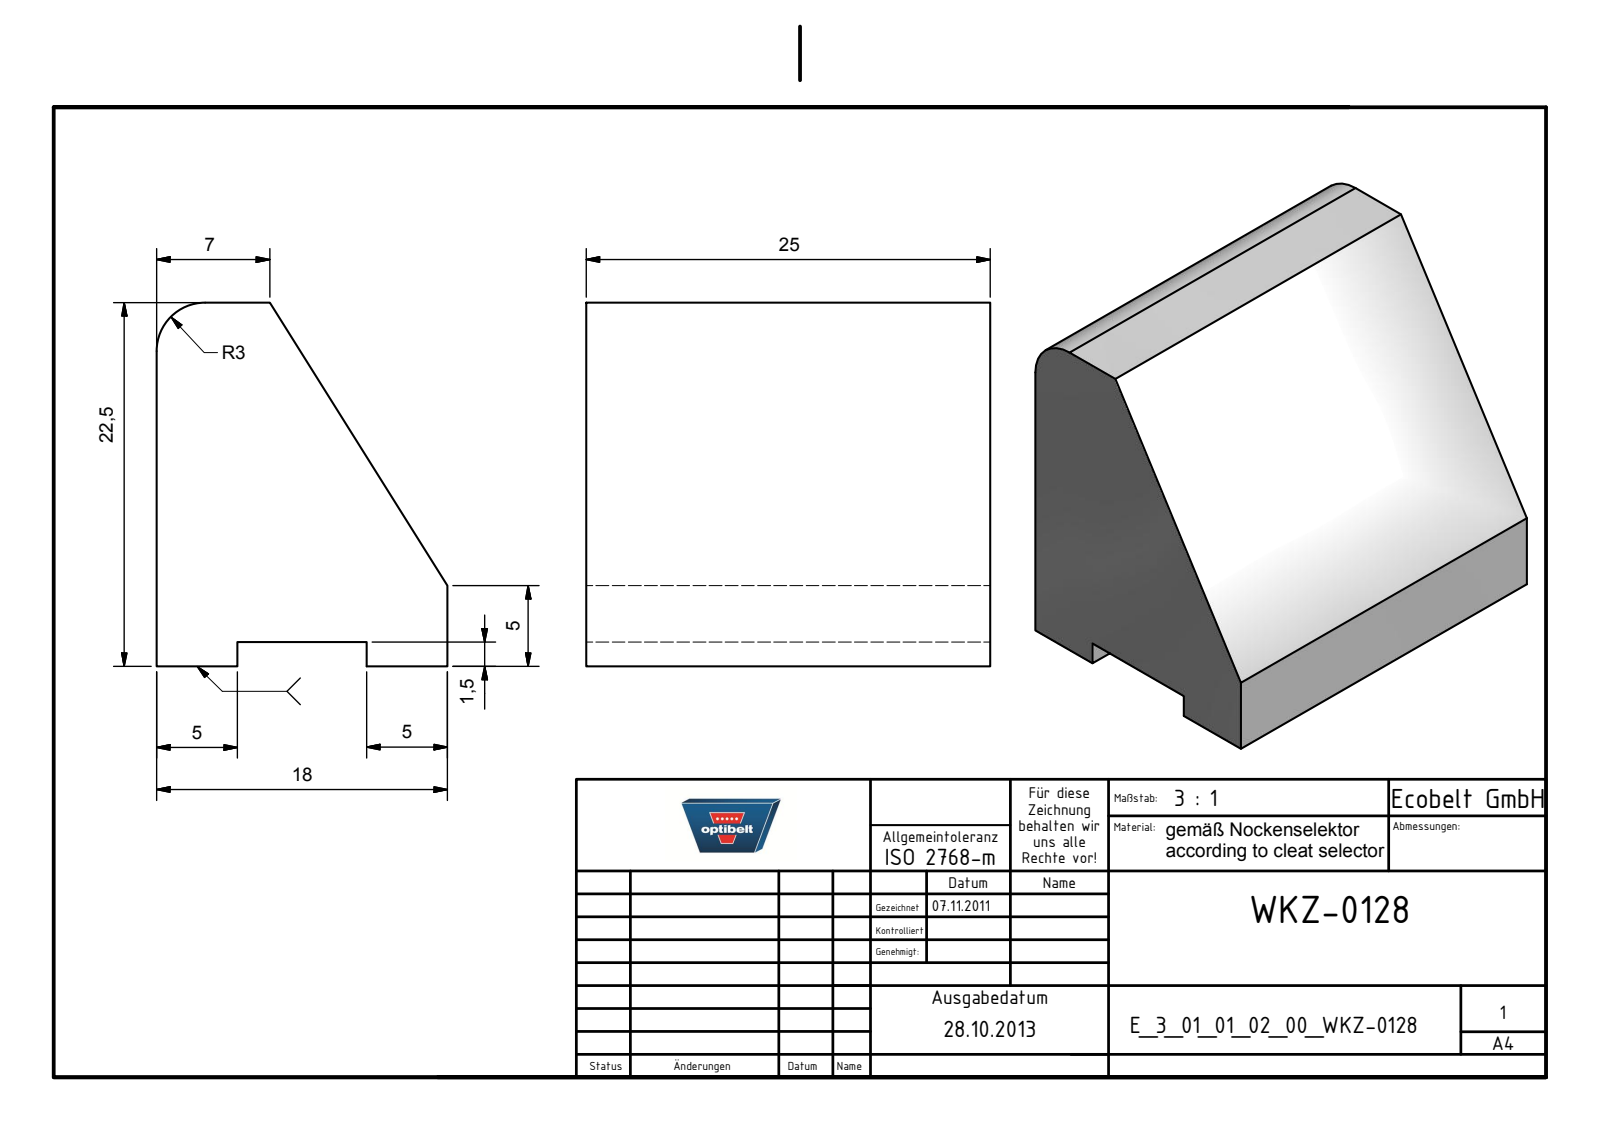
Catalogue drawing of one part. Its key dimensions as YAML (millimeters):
part_name: "E_3_01_01_02_00_WKZ-0128"
step_written_by: "Autodesk Inventor 2021 (AUTOMOTIVE_DESIGN)"
units: millimeters
bodies: {solids: 1, faces: 12, planar: 11, cylindrical: 1, other: 0}
overall_size: [25, 22.5, 18]
volume: 7370
surface_area: 2462
partial_cylinders:
  - {radius: 3, count: 1}
face_to_face_distances: [25, 1.5, 18, 22.5, 21, 5, 13, 8]
